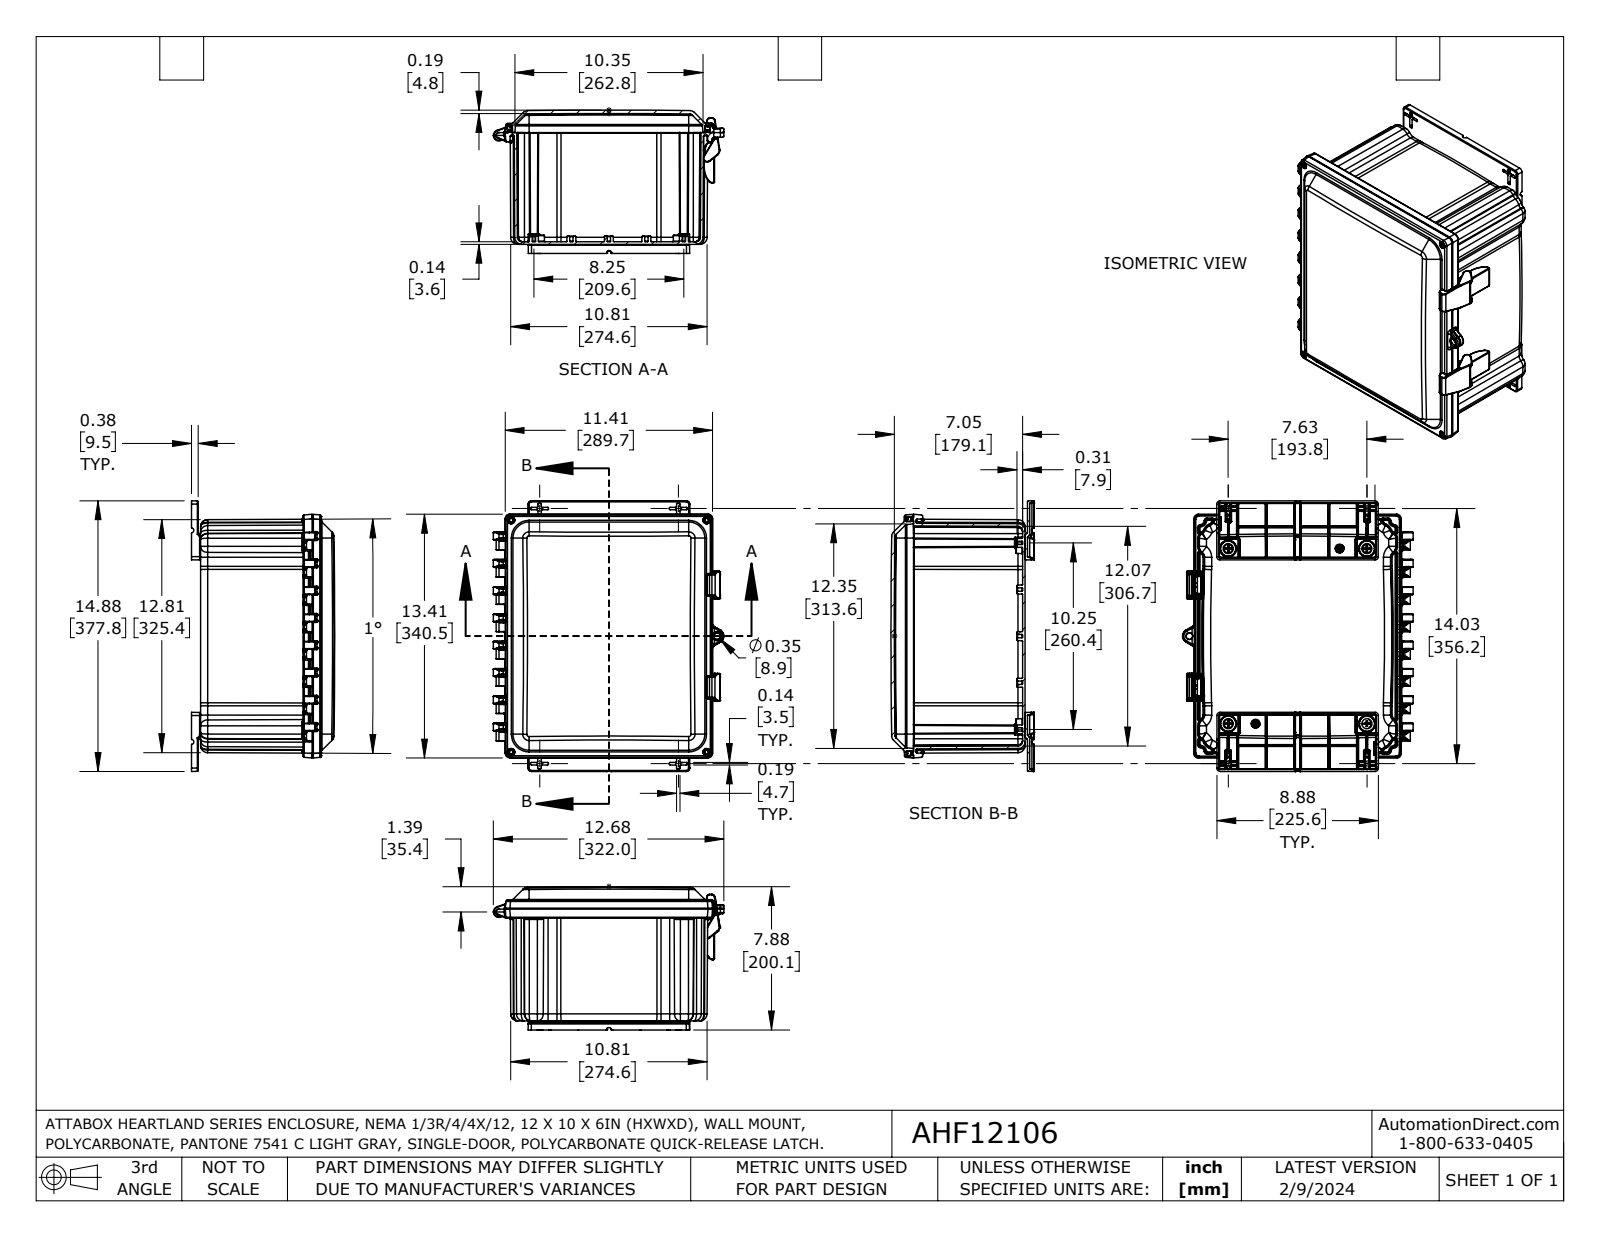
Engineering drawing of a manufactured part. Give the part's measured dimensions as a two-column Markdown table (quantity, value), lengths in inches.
| quantity | value |
| --- | --- |
| part name | AHF12106C |
| STEP written by | SolidWorks 2023 (AUTOMOTIVE_DESIGN) |
| units | inches |
| bodies | 6 solids, 1623 faces (528 planar, 521 cylindrical, 574 other) |
| overall size | 14.875 × 12.676 × 7.878 |
| volume | 134.3 in³ |
| surface area | 1 455 in² |
| round holes (diameter × count) | 0.187 × 21, 0.195 × 4, 0.249 × 4, 0.25 × 4, 0.27 × 4, 0.39 × 4, 0.327 × 1, 0.375 × 1, 0.45 × 1 |
| round bosses / shafts (diameter × count) | 0.487 × 21, 0.625 × 4, 0.25 × 4, 0.2 × 2 |
| partial cylindrical surfaces (radius × count) | 0.035 × 187, 0.065 × 25, 0.01 × 22, 0.02 × 21, 0.338 × 16, 0.05 × 8, 0.413 × 8, 0.09 × 4 |
| main face-to-face distances | 0.115, 0.14, 10.115, 0.5, 6.14, 12.115, 6.64, 10, 6, 0.29 |
| hole center spacings | 3.289, 2.563, 4.856, 6.697, 5.125, 5.524, 5.525, 6.579 |
